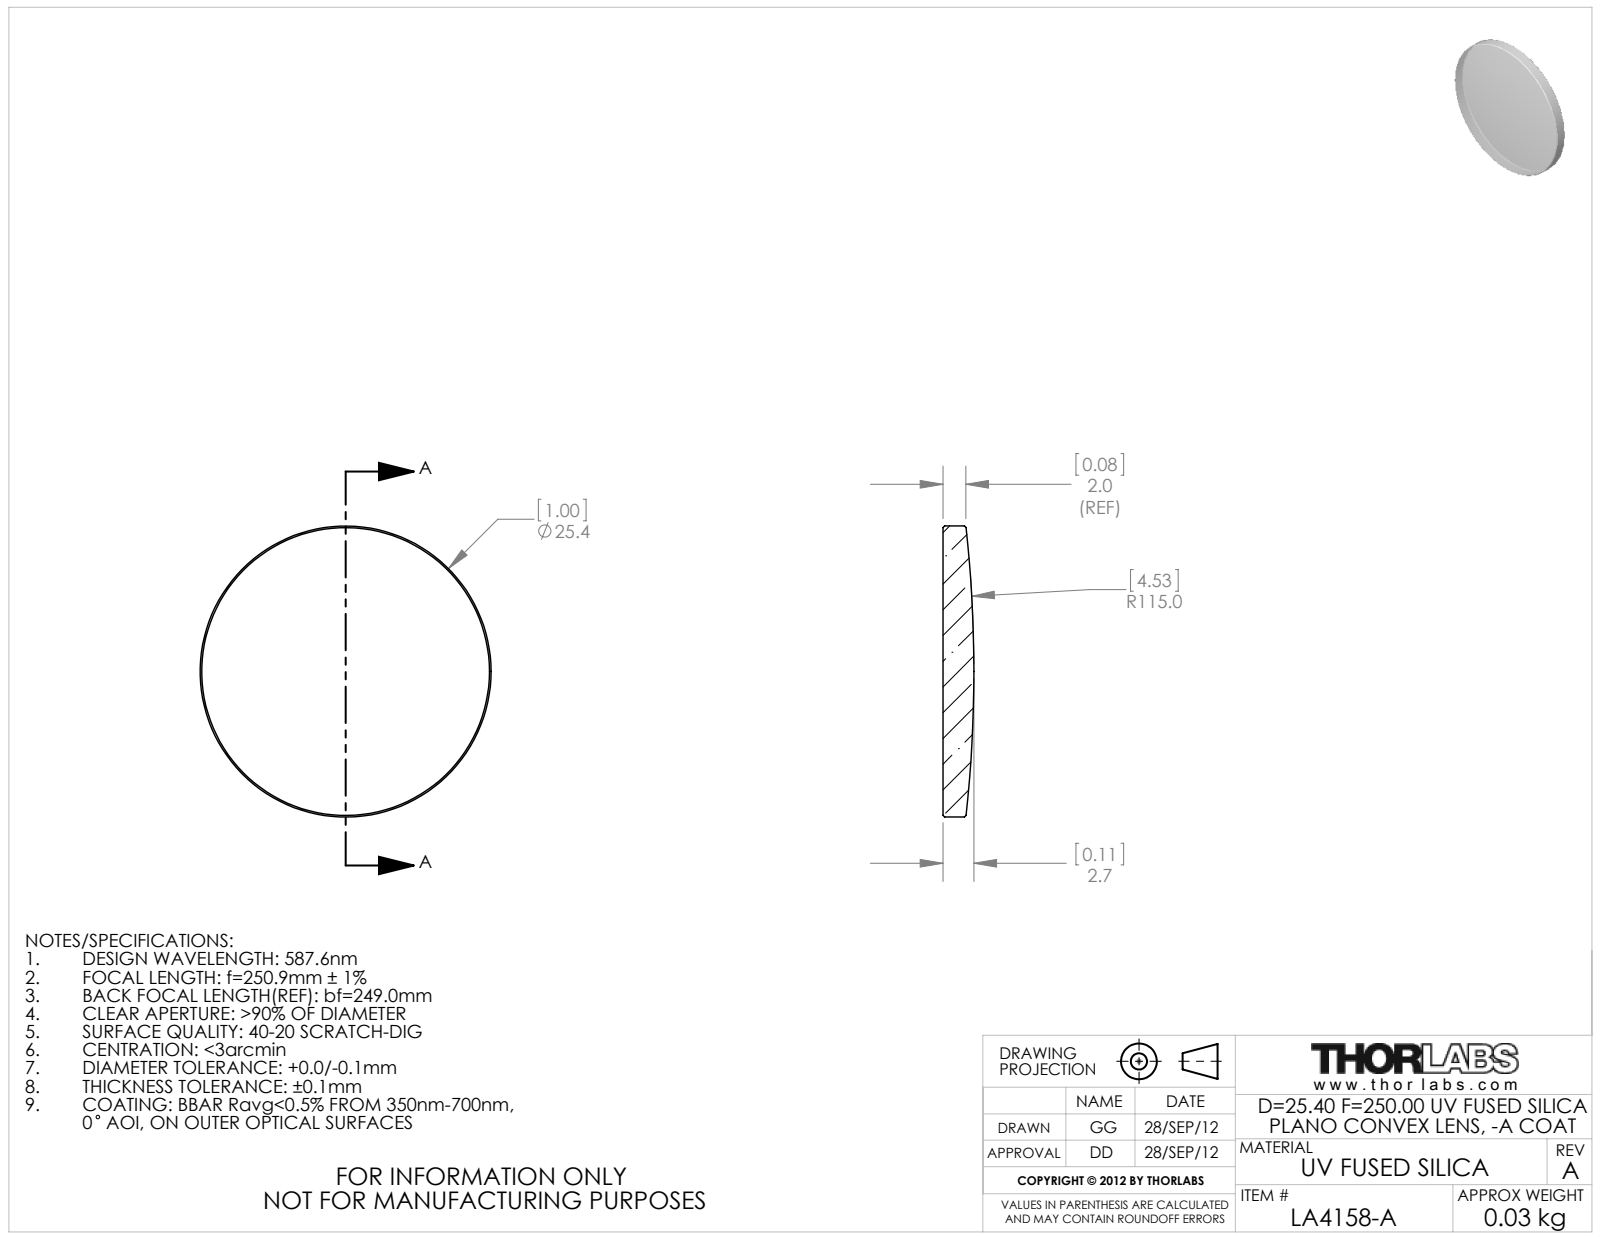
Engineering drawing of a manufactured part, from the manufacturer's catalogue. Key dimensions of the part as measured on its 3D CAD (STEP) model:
Part name (STEP PRODUCT): 25005-E0W
STEP written by: SolidWorks 2011 (CONFIG_CONTROL_DESIGN)
Units: millimetres
Bodies: 1 solid, 9 faces (1 planar, 2 cylindrical, 6 other)
Overall size (bounding box): 25.4 × 25.4 × 2.7
Volume: 1 190 mm³ · Surface area: 1 162 mm²
Round bosses / shafts (diameter × count): ⌀25.4 ×1
